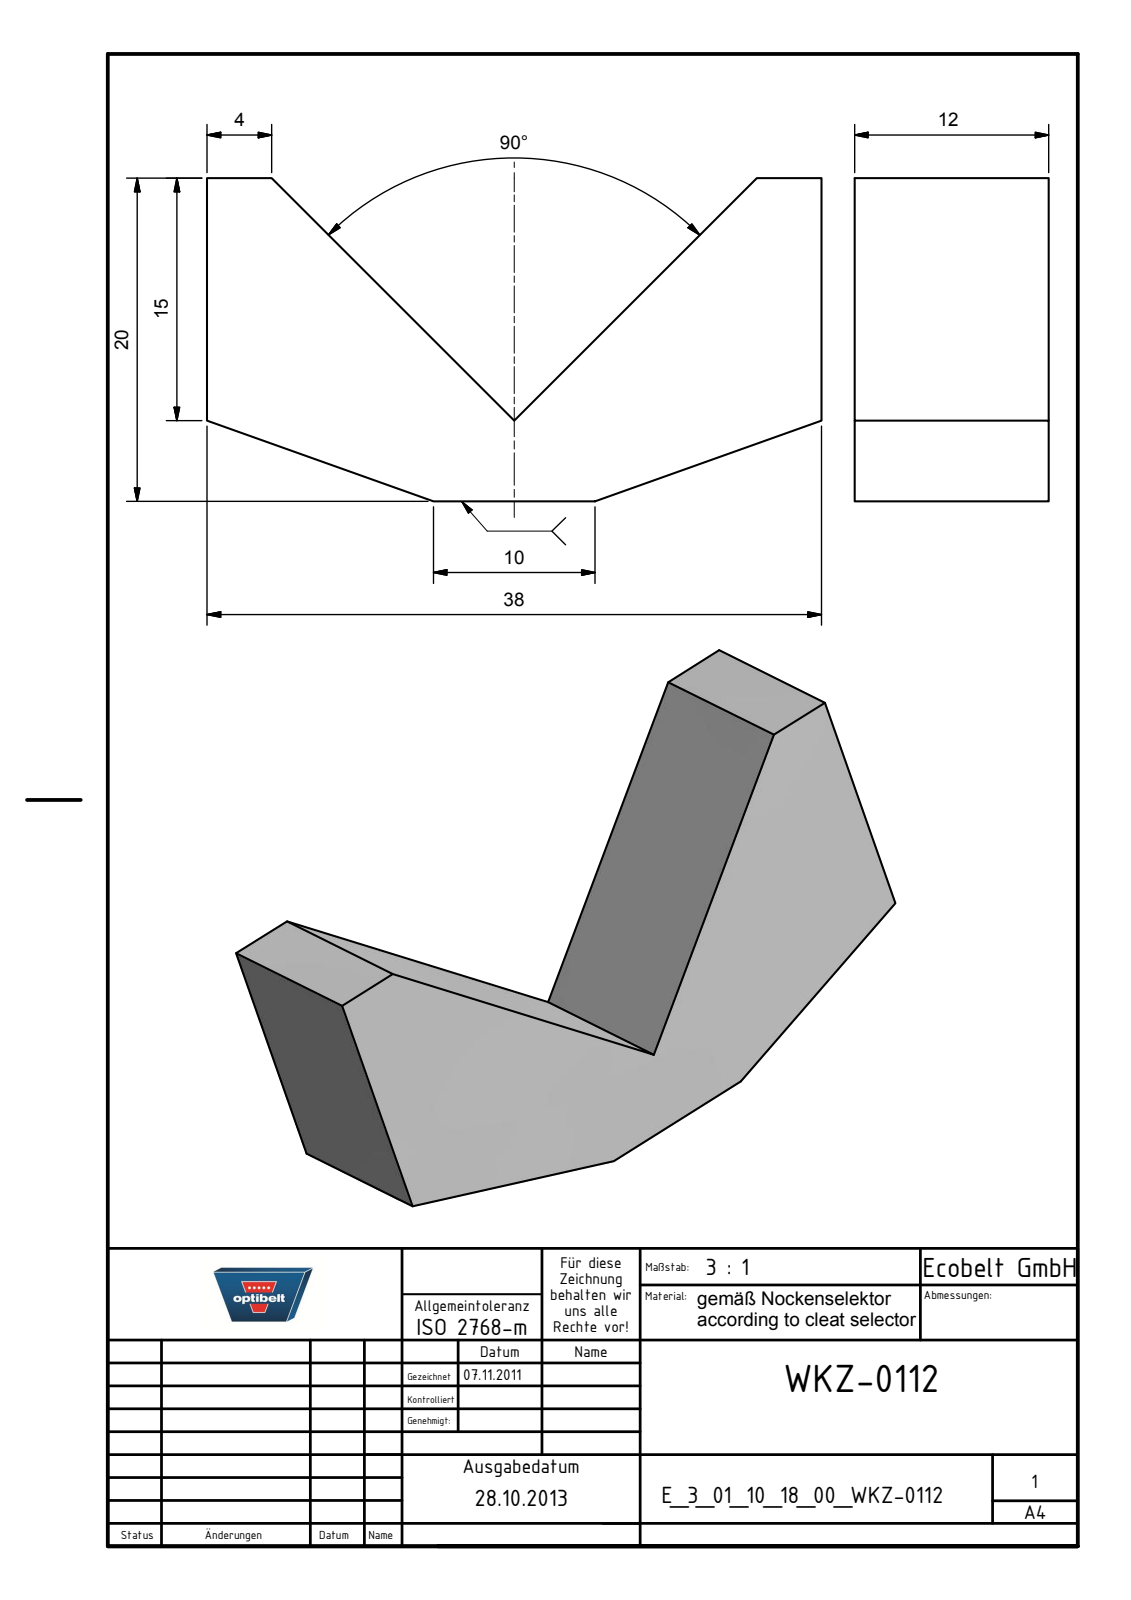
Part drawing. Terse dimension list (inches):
name: E_3_01_10_18_00_WKZ-0112
written by: Autodesk Inventor 2025 (AUTOMOTIVE_DESIGN)
unit: in
bodies: 1 solid, 11 faces (11 planar, 0 cylindrical, 0 other)
size: 1.496 × 0.787 × 0.472
volume: 0.341 in³; area: 3.677 in²
face distances: 0.472, 1.496, 0.787
